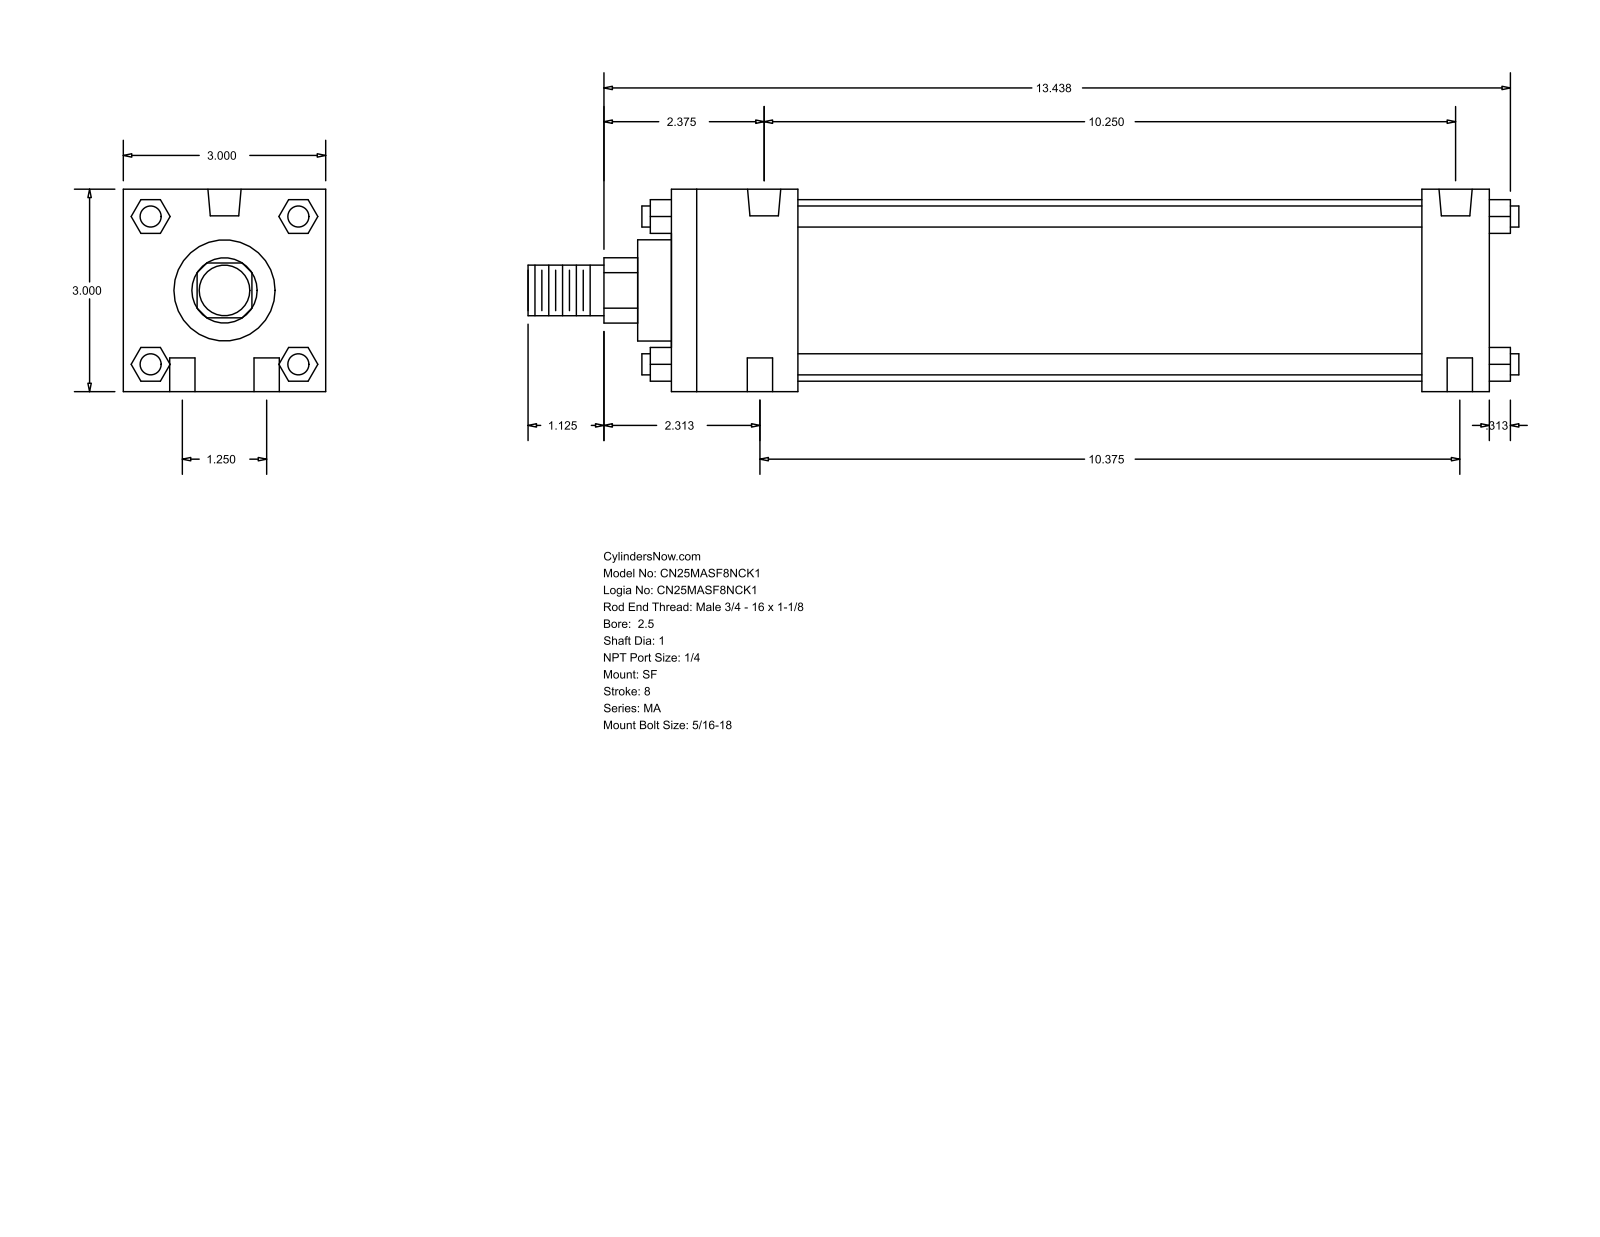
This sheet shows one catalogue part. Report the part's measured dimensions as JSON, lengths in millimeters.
{"part_name": "MA_SF__0250_1", "step_written_by": "GSSL Pune (CONFIG_CONTROL_DESIGN)", "units": "millimeters", "bodies": {"solids": 0, "faces": 124, "planar": 94, "cylindrical": 30, "other": 0}, "overall_size": [373.06, 76.2, 76.2], "round_holes": [[9.53, 4], [7.94, 2], [12.49, 2]], "round_bosses_or_shafts": [[7.94, 4], [68.33, 1], [38.1, 1], [25.4, 1], [19.05, 1]], "partial_cylinders_radius": [[12.29, 1]], "face_to_face_distances": [76.2, 307.98, 12.7, 25.4, 282.58, 47.63, 234.95, 260.35, 27.81, 48.17], "hole_center_spacings": [15.96, 31.76, 260.35, 262.41, 262.42, 263.52, 265.43]}
